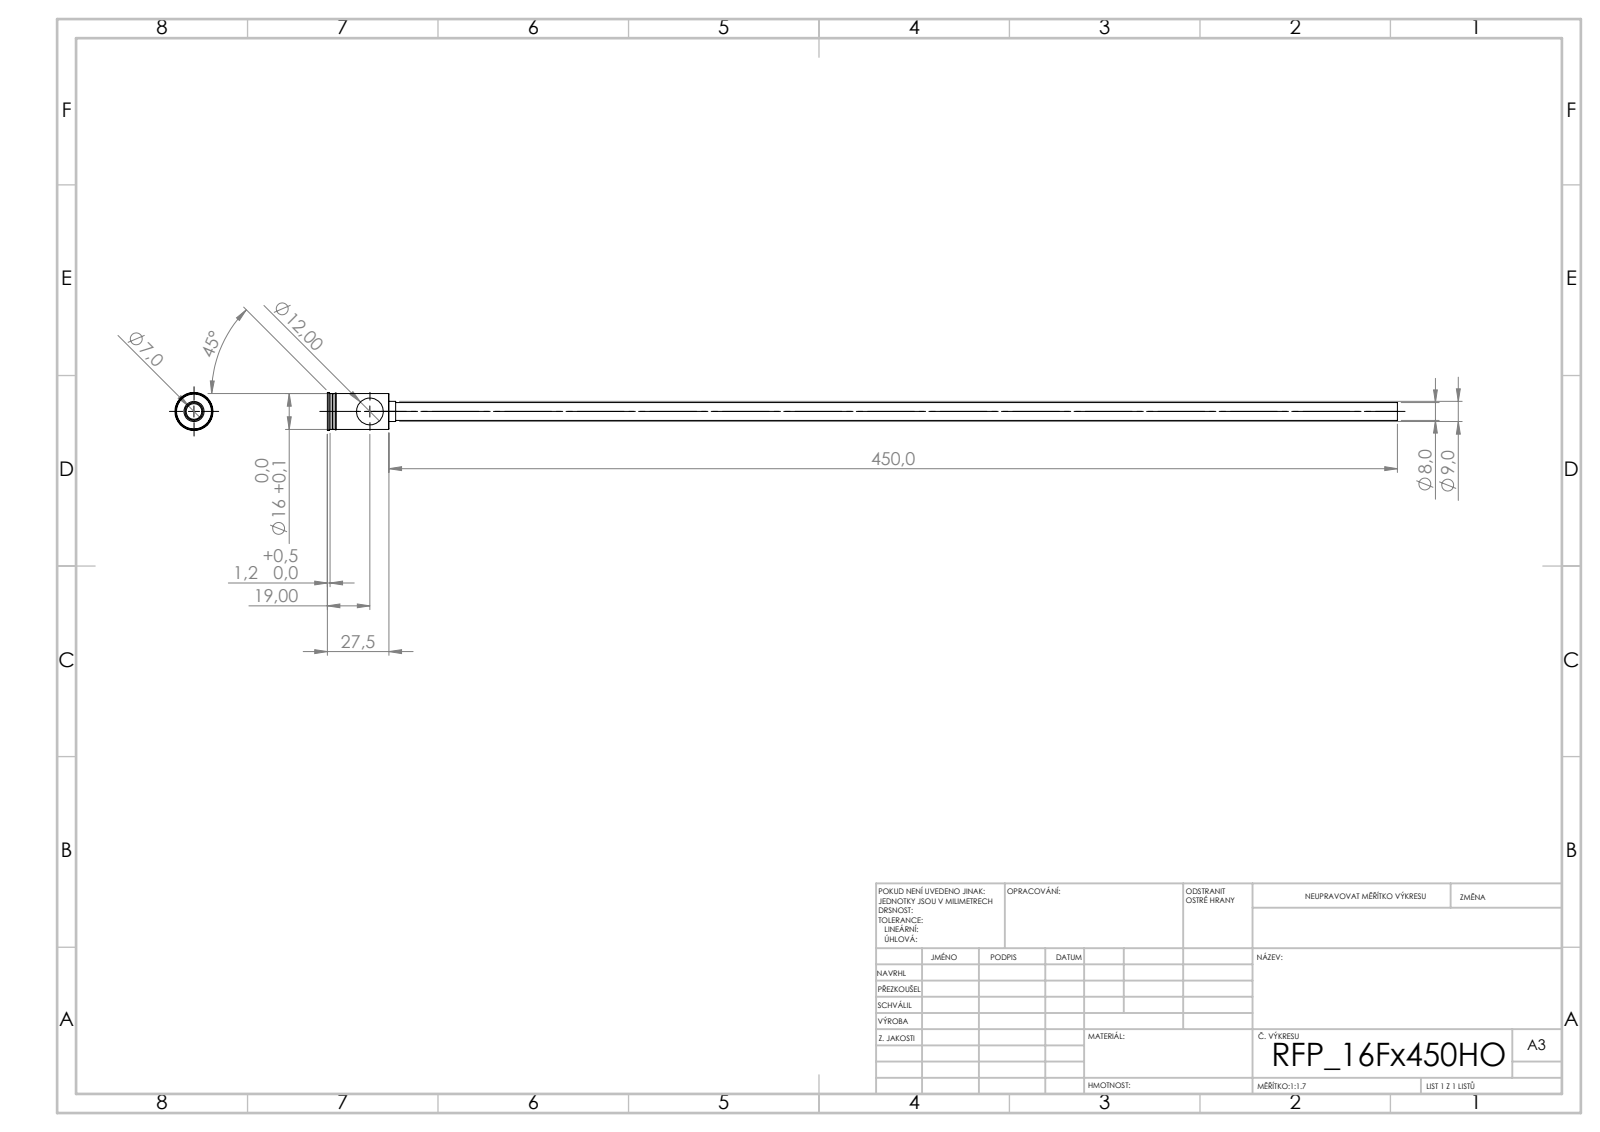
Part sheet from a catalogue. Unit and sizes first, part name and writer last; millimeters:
Units: millimetres
Overall size (bounding box): 477.5 × 17 × 17
Round holes (diameter × count): ⌀7 ×1, ⌀12 ×1
Round bosses / shafts (diameter × count): ⌀17 ×1, ⌀16 ×1, ⌀9 ×1, ⌀8 ×1
Main face-to-face distances: 25.5, 2, 27.5, 11.4, 0.5, 25, 2.5, 3, 28, 28.5
Volume: 8 895 mm³ · Surface area: 23 396 mm²
Bodies: 1 solid, 44 faces (20 planar, 16 cylindrical, 8 other)
STEP written by: SolidWorks 2019 (CONFIG_CONTROL_DESIGN)
